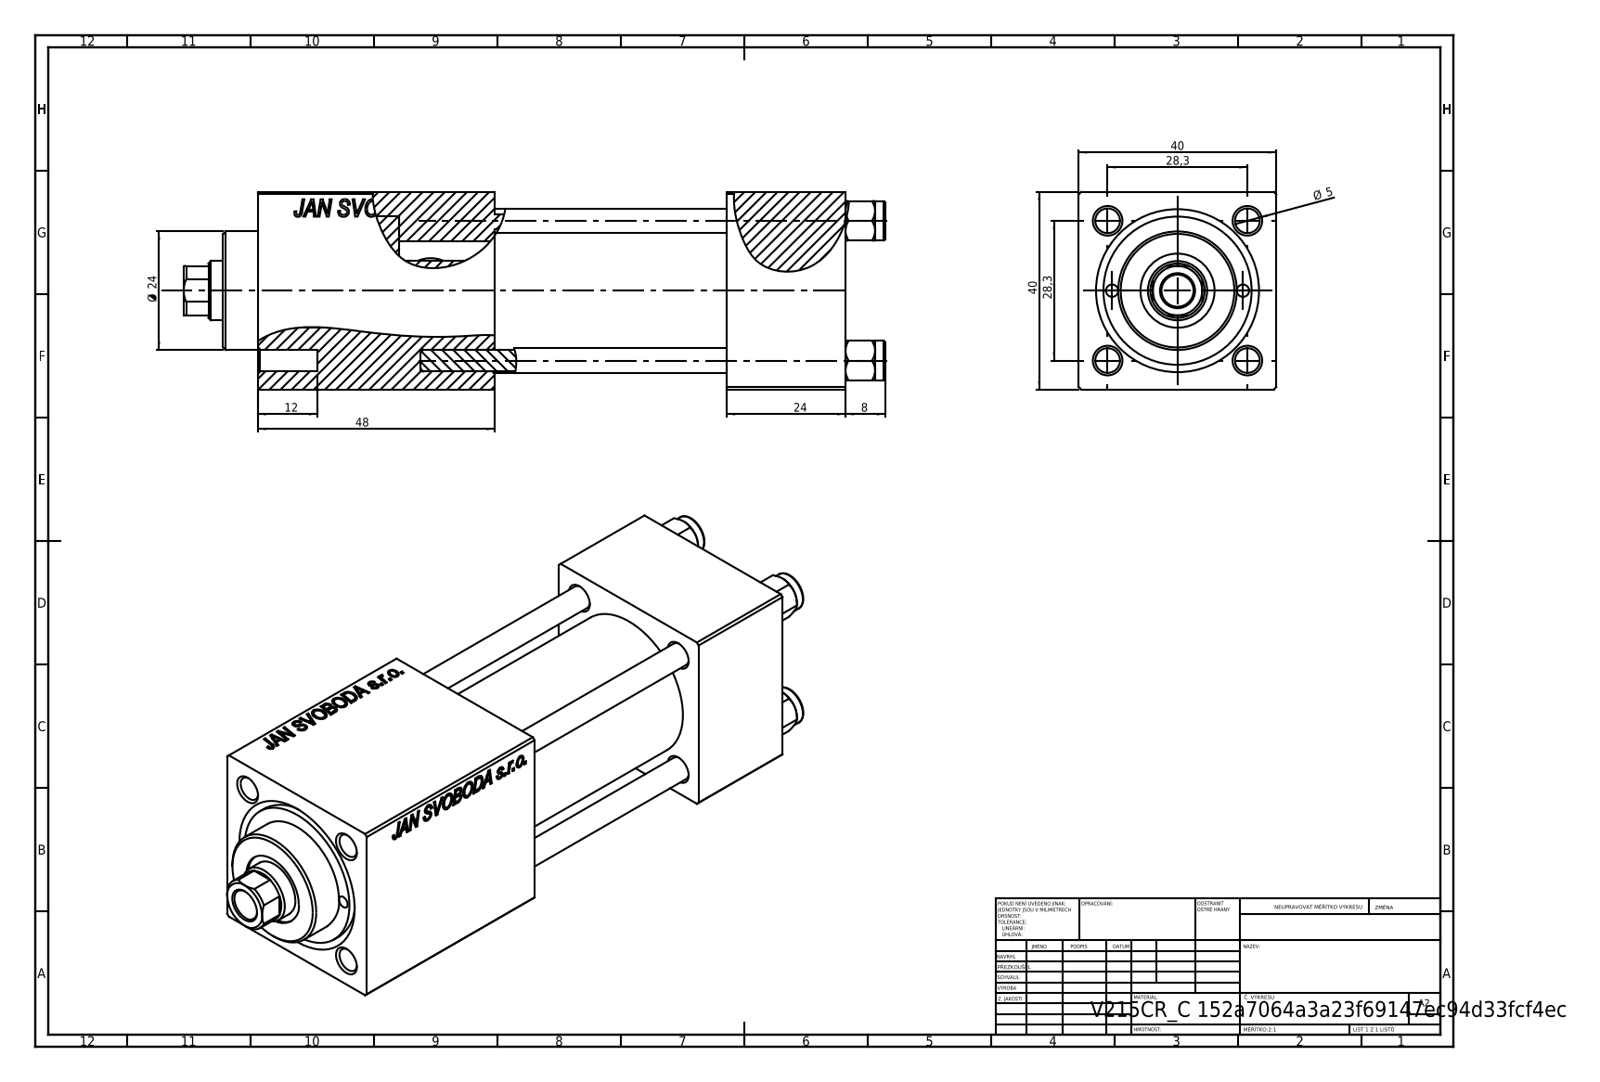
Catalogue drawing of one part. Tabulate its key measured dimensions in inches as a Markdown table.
| quantity | value |
| --- | --- |
| part name | NUT_M5_C; V215CR_VCP_C; V215CR_C_TYCINKA; V215CR_C_Body (+1 more) |
| STEP written by | SolidWorks 2019 (CONFIG_CONTROL_DESIGN) |
| units | inches |
| bodies | 11 solids, 1153 faces (527 planar, 90 cylindrical, 536 other) |
| overall size | 5.591 × 1.575 × 1.575 |
| volume | 8.686 in³ |
| surface area | 84.51 in² |
| round holes (diameter × count) | 0.197 × 4, 0.787 × 3, 0.098 × 2, 0.276 × 2, 0.518 × 2, 0.256 × 1, 0.472 × 1, 0.591 × 1, 0.984 × 1, 1.181 × 1 |
| round bosses / shafts (diameter × count) | 0.315 × 4, 1.22 × 1, 0.945 × 1 |
| partial cylindrical surfaces (radius × count) | 0.217 × 1 |
| main face-to-face distances | 1.575, 0.945, 3.555, 2.61, 1.89, 2.795, 1.85, 0.76, 4.685, 3.74 |
| hole center spacings | 0.558, 0.788, 1.114, 1.214, 0.522, 1.576, 1.043, 2.835 |
